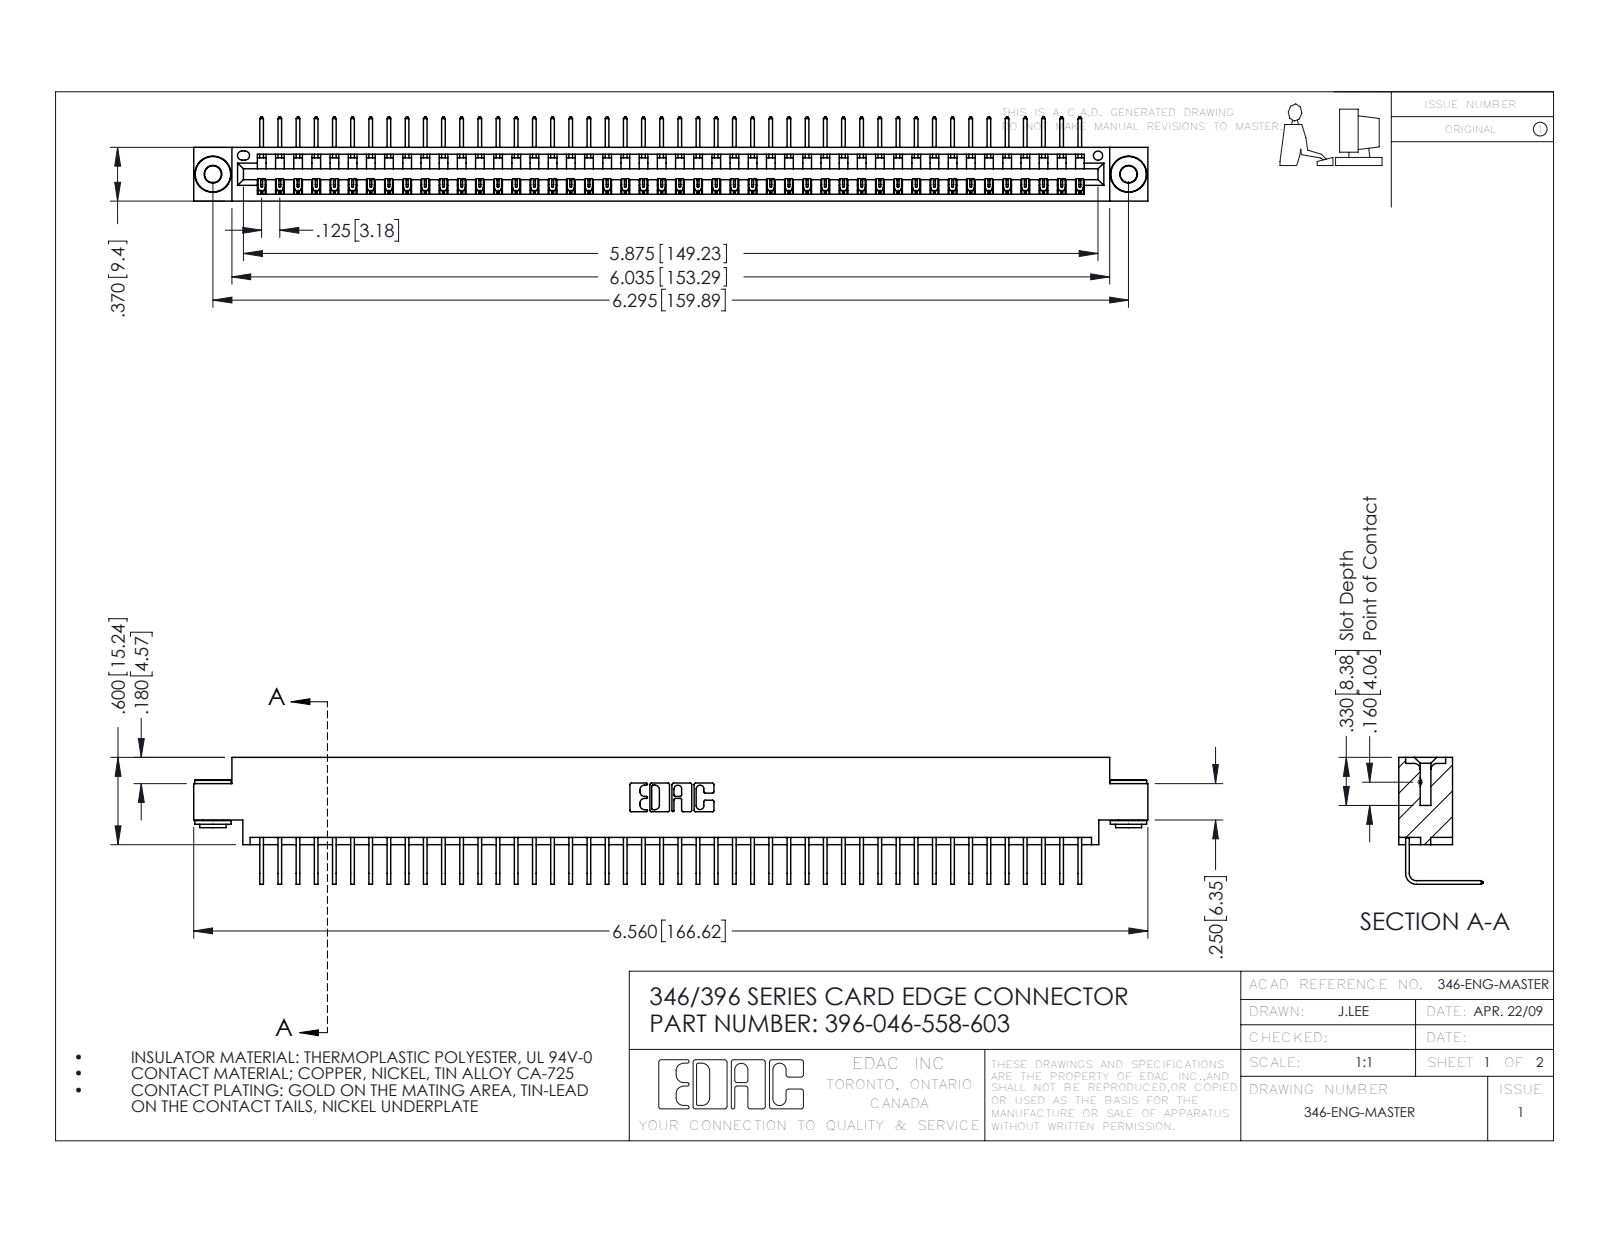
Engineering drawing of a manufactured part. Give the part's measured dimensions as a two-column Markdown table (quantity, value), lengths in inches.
| quantity | value |
| --- | --- |
| part name | 346 Part_0.170 Offset - 0.156 Dia-TH; 396-046-558-603; 345-250-002_345-250-002-102; 345-292-001_558 Tail - 2 |
| STEP written by | SolidWorks 2016 (CONFIG_CONTROL_DESIGN) |
| units | inches |
| bodies | 49 solids, 2924 faces (2022 planar, 894 cylindrical, 8 other) |
| overall size | 6.56 × 0.873 × 0.58 |
| volume | 0.976 in³ |
| surface area | 33.06 in² |
| round holes (diameter × count) | 0.116 × 2, 0.156 × 2, 0.064 × 1 |
| round bosses / shafts (diameter × count) | 0.25 × 2, 0.18 × 2, 0.136 × 2 |
| partial cylindrical surfaces (radius × count) | 0.006 × 92, 0.01 × 22, 0.007 × 6, 0.031 × 6, 0.026 × 3, 0.031 × 2, 0.04 × 2, 0.014 × 1 |
| main face-to-face distances | 0.322, 0.048, 0.37, 0.25, 0.025, 0.298, 0.072, 0.148, 0.222, 0.1 |
| hole center spacings | 0.246, 6.086, 6.295 |
